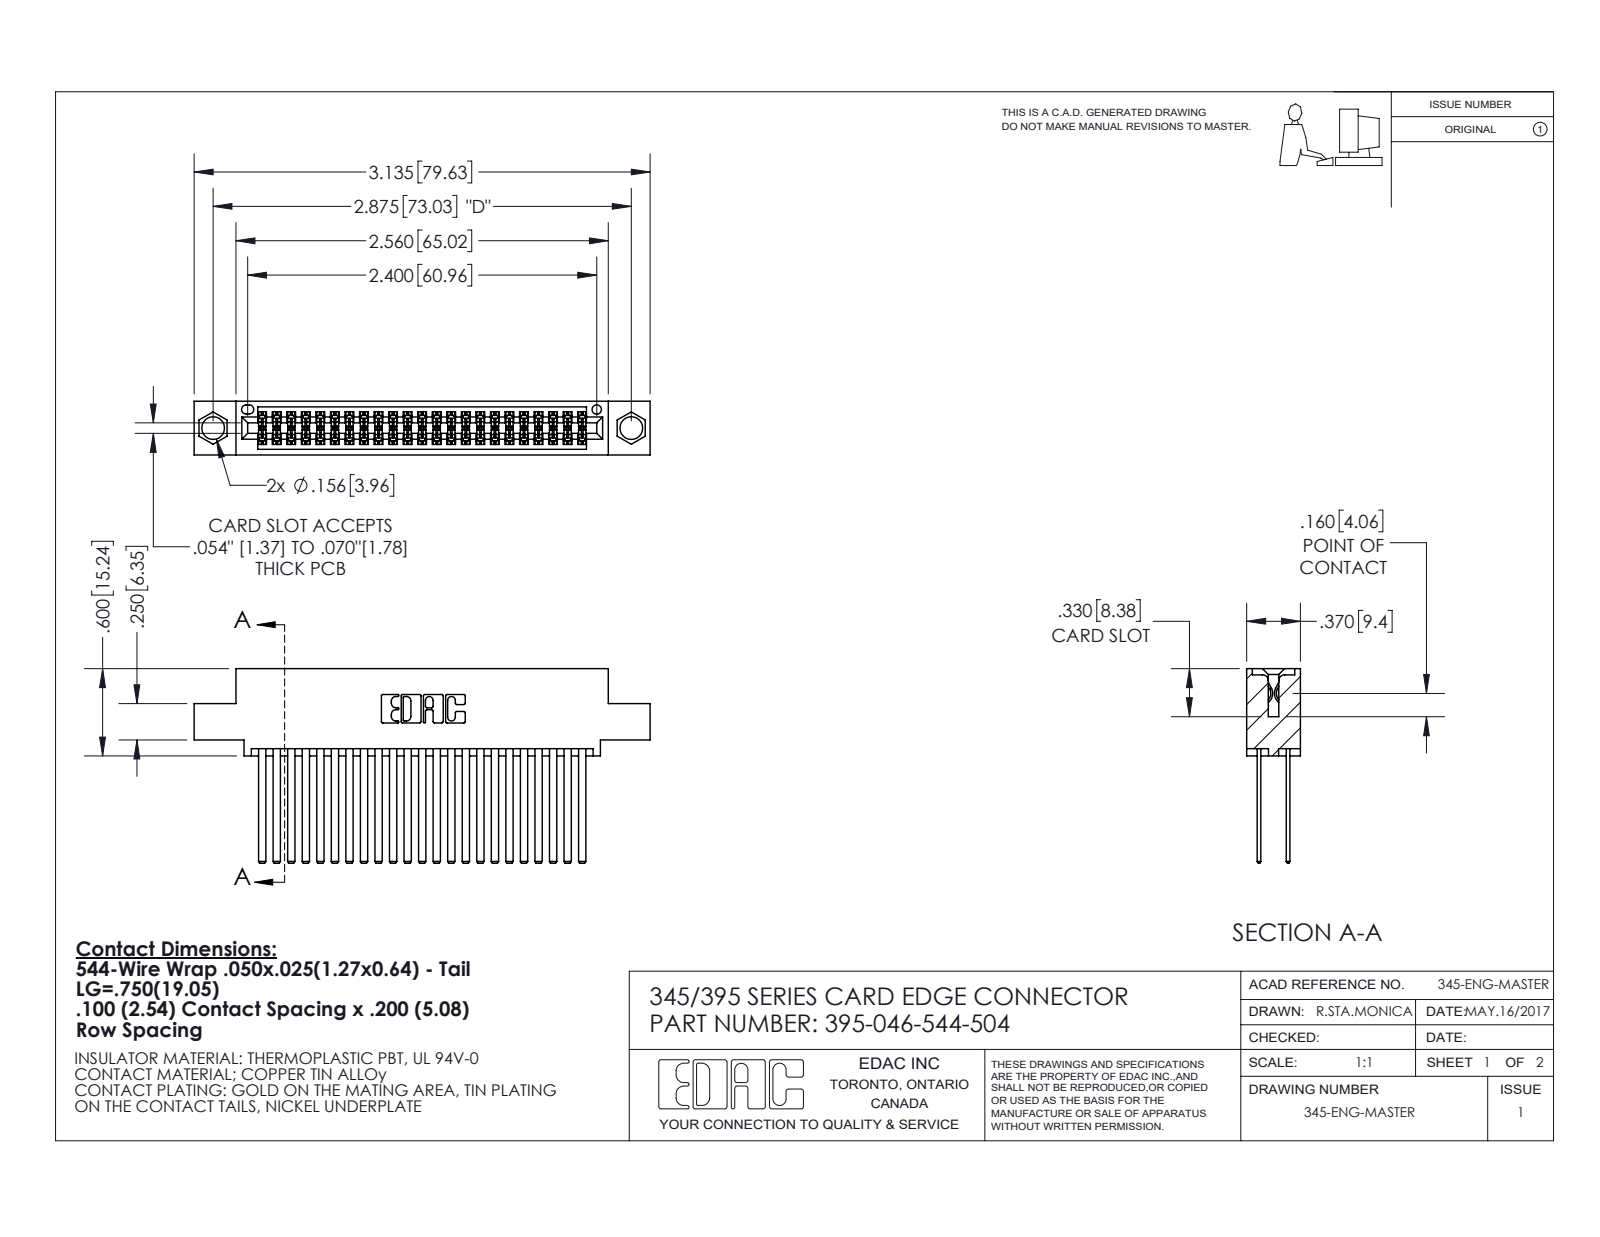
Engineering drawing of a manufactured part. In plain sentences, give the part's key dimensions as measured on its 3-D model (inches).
The part is named "345-292-001_345-293-144; 345 Part_0.110 Offset - 0.156 Dia-TI; 395-046-544-504". Its 3-D file was written by "SolidWorks 2020 (CONFIG_CONTROL_DESIGN)". It is 47 solids with 2168 faces: 1432 planar, 736 cylindrical and 0 other. Overall it measures 3.135 by 1.337 by 0.37 inches. Its volume is 0.49 cubic inches and its surface area 20.66 square inches. Round holes: 2 of diameter 0.156, 1 of diameter 0.064. Partial cylindrical surfaces (rounded edges, fillets, slot ends): 92 of radius 0.006, 22 of radius 0.01, 6 of radius 0.007, 6 of radius 0.031, 3 of radius 0.026, 2 of radius 0.014, 2 of radius 0.019, 2 of radius 0.022. The main face-to-face distances are 0.2, 0.072, 0.298, 0.025, 0.098, 0.272, 0.225, 0.175, 0.37, 0.05. The hole center spacings are 0.27, 2.641, 2.875.
